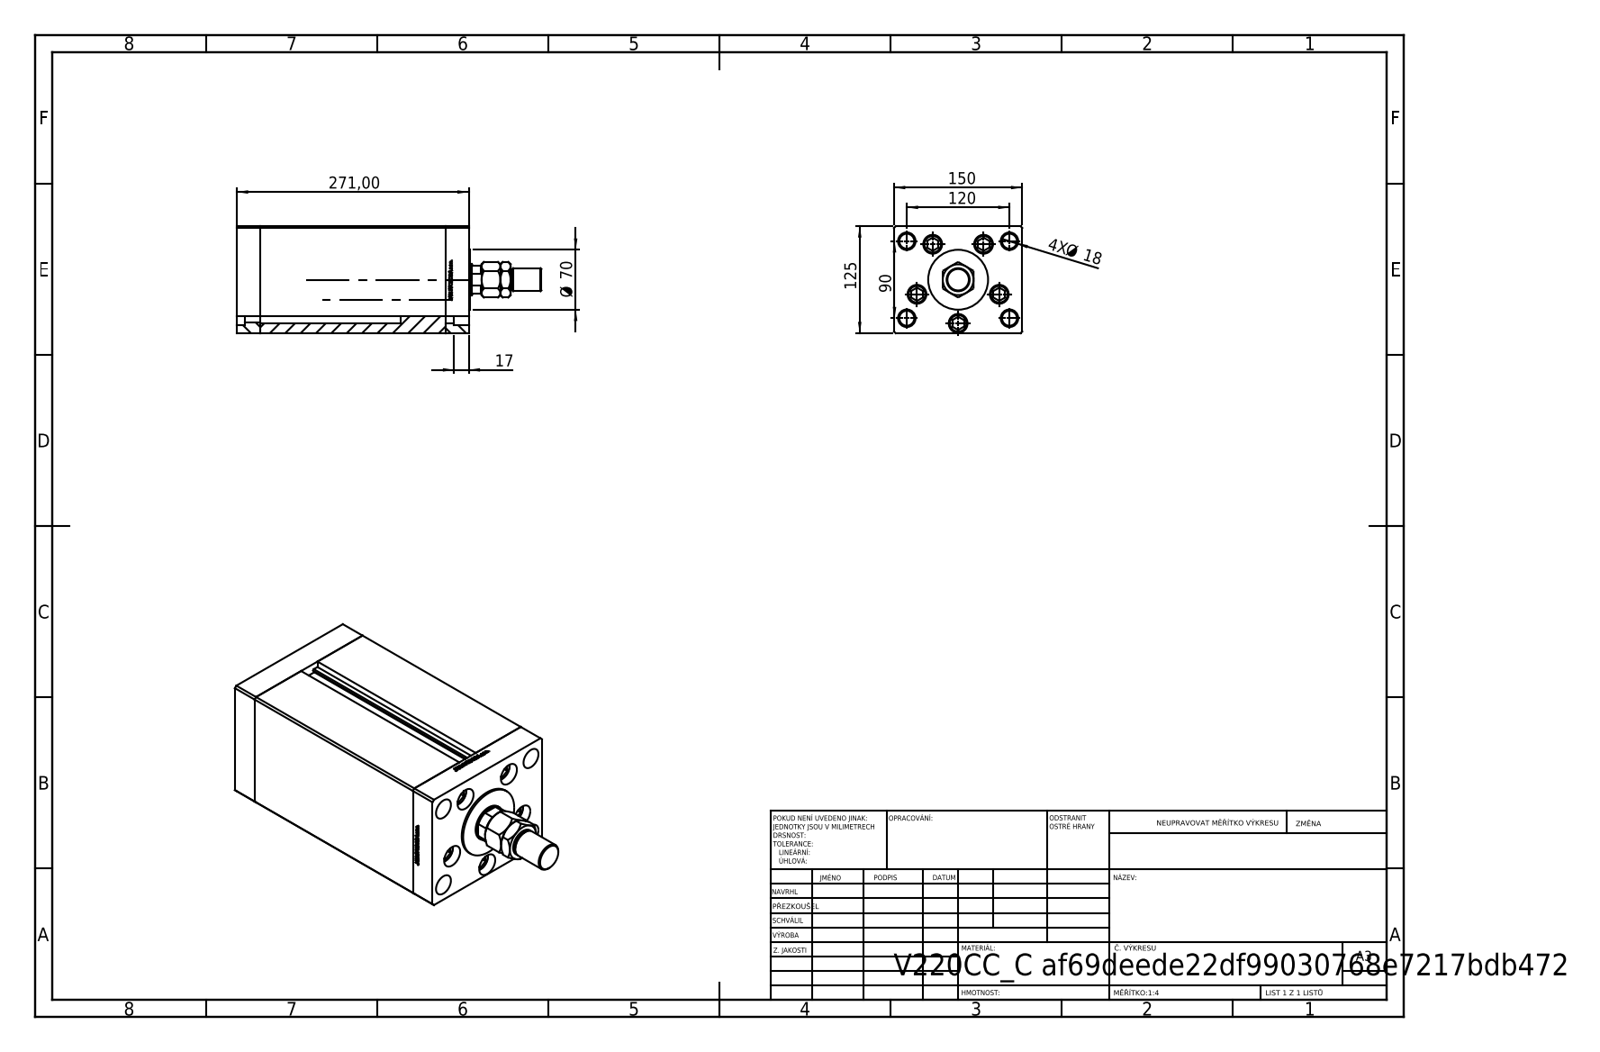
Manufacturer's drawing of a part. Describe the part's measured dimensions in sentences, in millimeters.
The part is named "V220C_VC_C; V220C FRONT; V220C_C MIDDLE; MTA (+2 more)". Its 3-D file was written by "SolidWorks 2019 (CONFIG_CONTROL_DESIGN)". It is 14 solids with 1212 faces: 557 planar, 163 cylindrical and 492 other. Overall it measures 356 by 150 by 125 millimeters. Its volume is 4 186 000 cubic millimeters and its surface area 459 325 square millimeters. Round holes: 9 of diameter 17.5, 5 of diameter 22, 4 of diameter 16, 4 of diameter 20.5, 1 of diameter 21, 1 of diameter 25.5, 1 of diameter 36. Round bosses or shafts: 5 of diameter 8, 4 of diameter 21, 1 of diameter 80, 1 of diameter 70, 1 of diameter 27, 1 of diameter 25. Partial cylindrical surfaces (rounded edges, fillets, slot ends): 2 of radius 0.93, 1 of radius 17.5. The main face-to-face distances are 150, 125, 27, 244, 217, 33.5, 6.5, 271, 237.5, 210.5. The hole center spacings are 51, 75, 30.43, 30.48, 58.89, 60.3, 61.25, 63.14.
